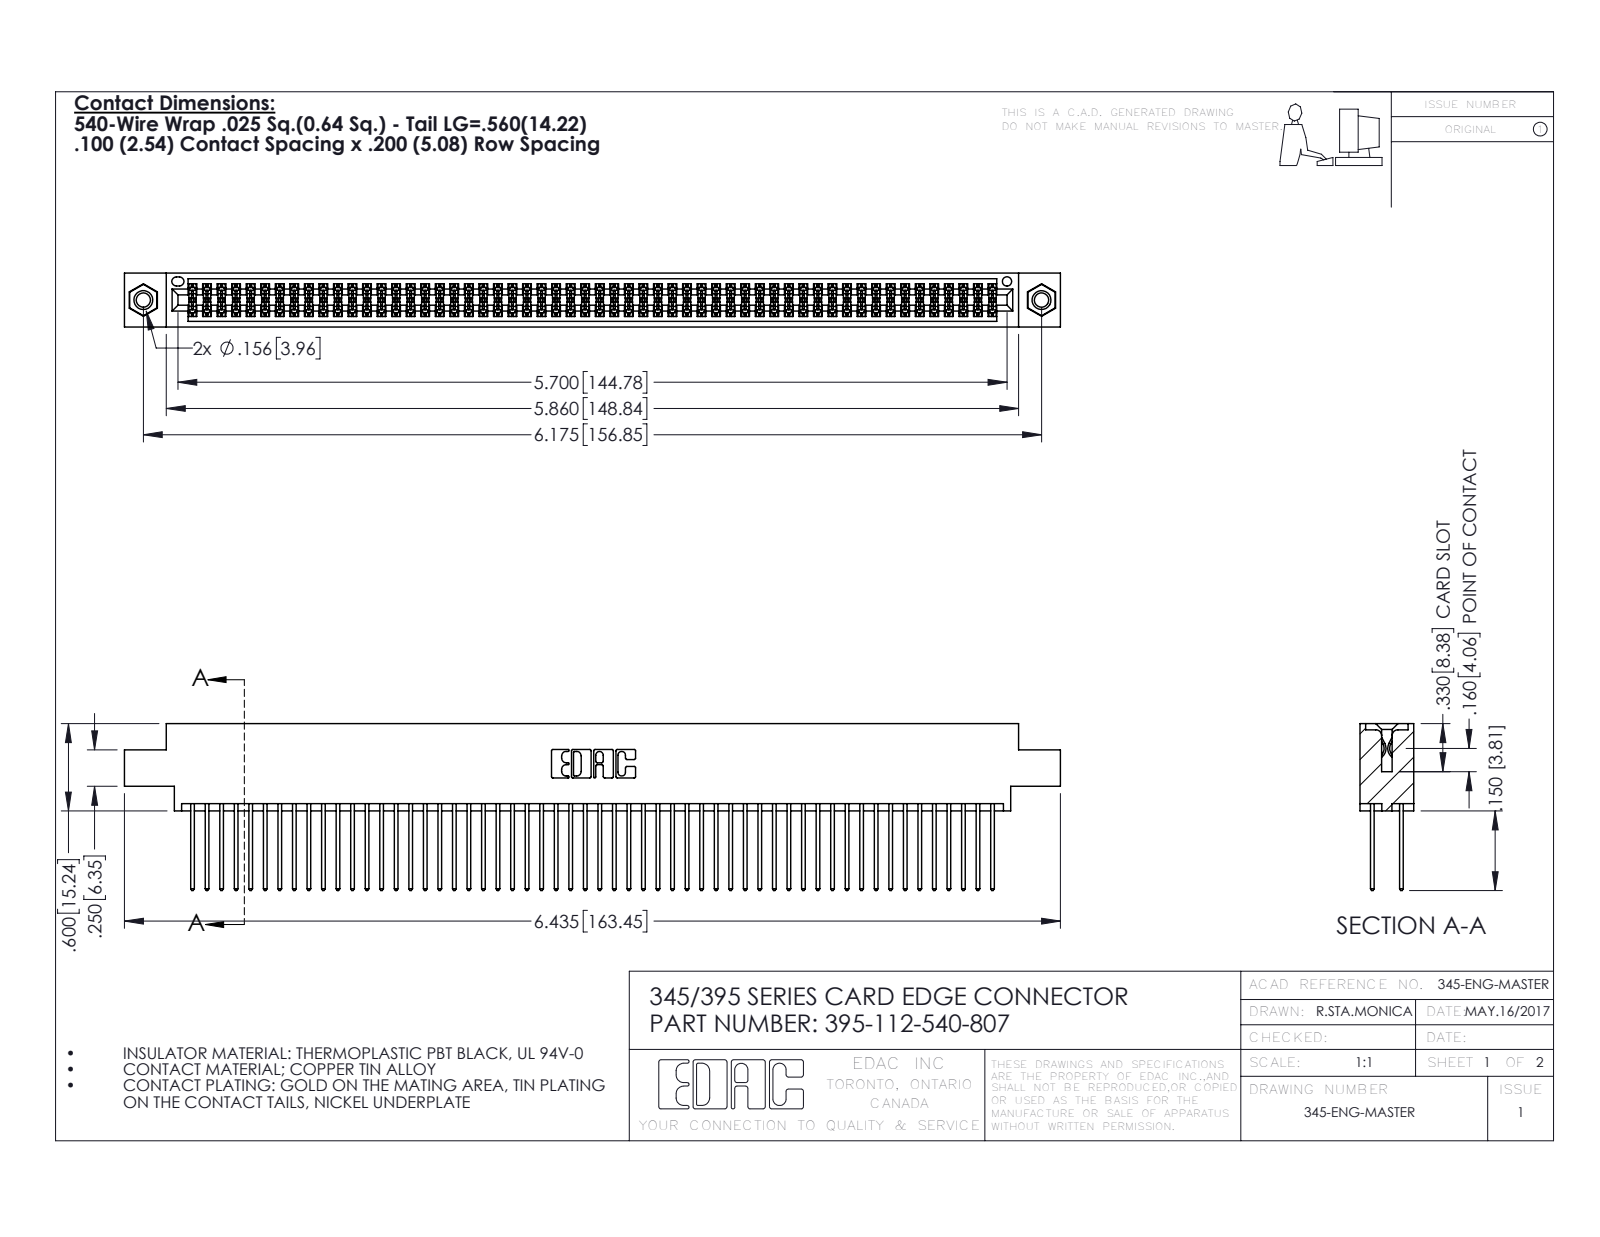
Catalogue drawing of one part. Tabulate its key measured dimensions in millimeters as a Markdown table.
| quantity | value |
| --- | --- |
| part name | 395-112-540-807; 345 Part_0.170 Offset - 0.156 Dia-TI; 345-250-001_345-250-005-103; 345-292-001_345-293-140 |
| STEP written by | SolidWorks 2016 (CONFIG_CONTROL_DESIGN) |
| units | millimeters |
| bodies | 115 solids, 5790 faces (3812 planar, 1962 cylindrical, 16 other) |
| overall size | 163.4 × 29.1 × 9.4 |
| volume | 16 300 mm³ |
| surface area | 26 520 mm² |
| round holes (diameter × count) | 2.5 × 2, 3.2 × 2, 4 × 2, 1.6 × 1 |
| round bosses / shafts (diameter × count) | 3.9 × 2 |
| partial cylindrical surfaces (radius × count) | 0.2 × 168, 0.3 × 112, 0.3 × 22, 0.2 × 6, 0.8 × 6, 0.7 × 3, 0.4 × 2, 0.5 × 2 |
| main face-to-face distances | 1.8, 7.6, 5.1, 2.5, 6.9, 0.6, 9.4, 5.7, 4.4, 3.8 |
| hole center spacings | 6.9, 150.9, 156.8 |
